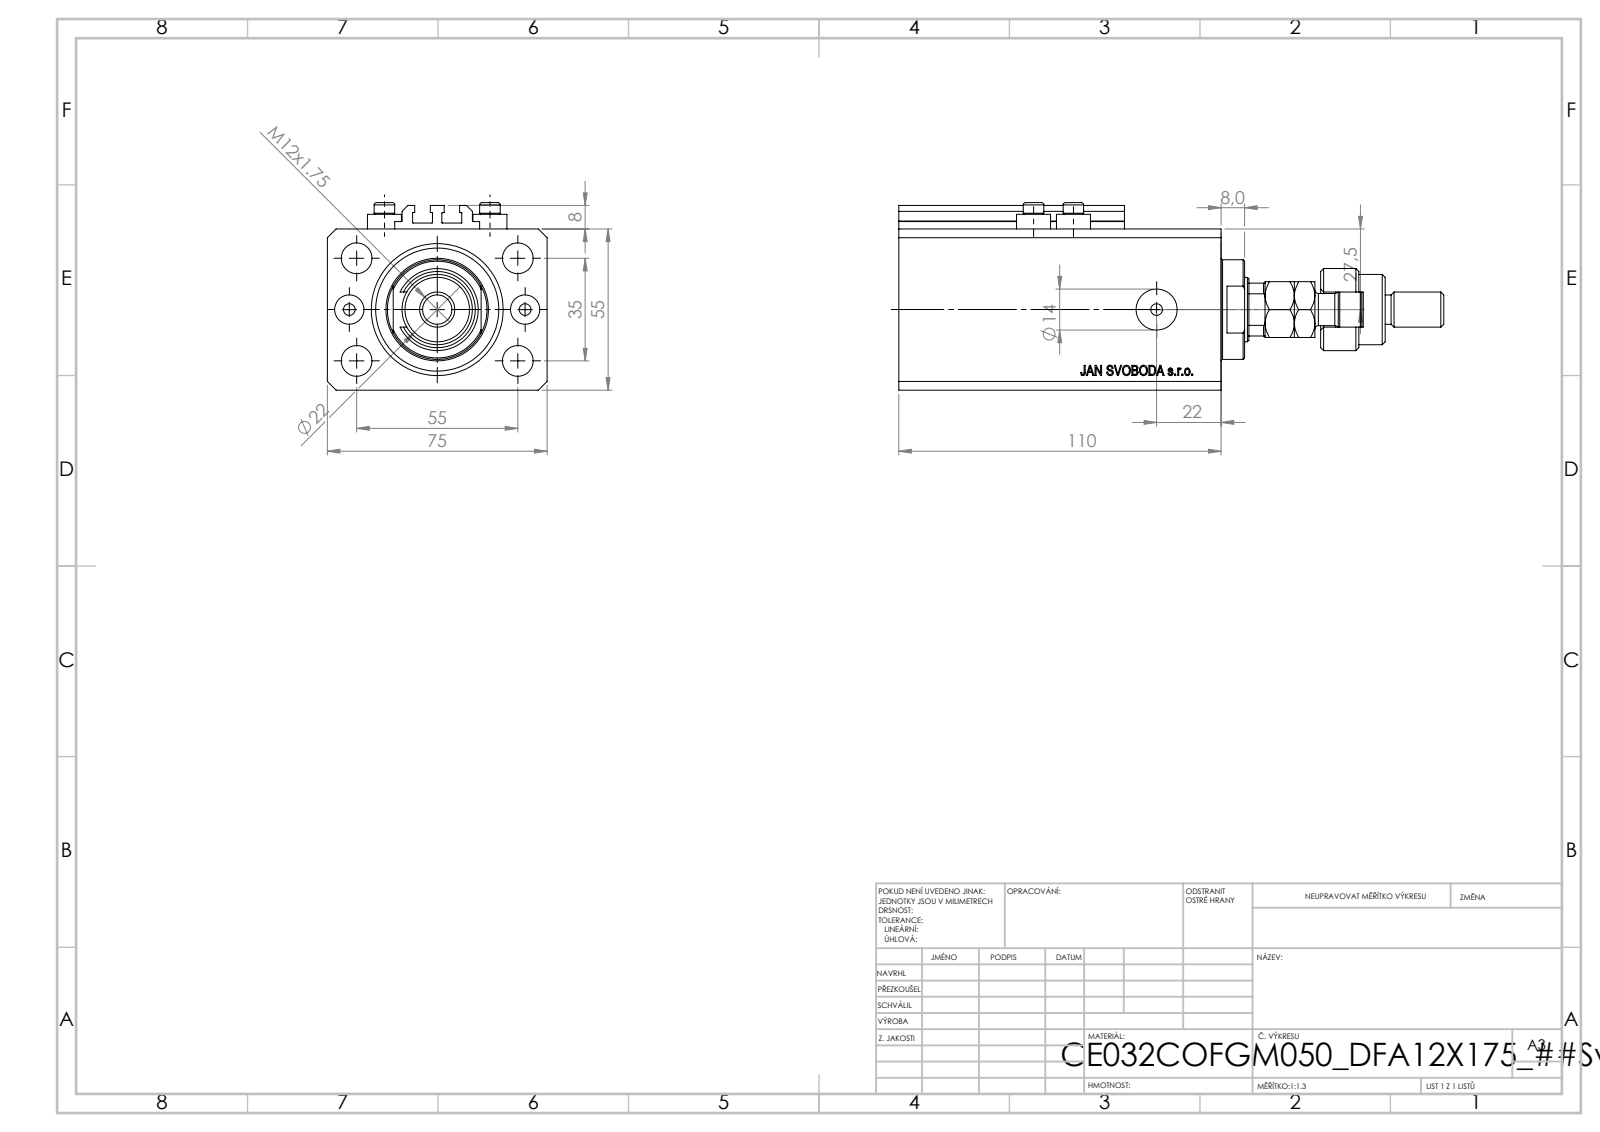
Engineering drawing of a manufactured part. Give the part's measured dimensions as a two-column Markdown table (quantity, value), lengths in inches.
| quantity | value |
| --- | --- |
| part name | V250CE_C_Body; V250CE_VC_C; ALLEN BOLT V250CE; V250CE_C_VCP (+2 more) |
| STEP written by | SolidWorks 2019 (CONFIG_CONTROL_DESIGN) |
| units | inches |
| bodies | 10 solids, 1119 faces (532 planar, 99 cylindrical, 488 other) |
| overall size | 7.323 × 2.953 × 2.52 |
| volume | 26.05 in³ |
| surface area | 152.3 in² |
| round holes (diameter × count) | 0.157 × 8, 0.413 × 5, 0.394 × 2, 0.551 × 2, 0.866 × 1, 1.26 × 1, 1.772 × 1 |
| round bosses / shafts (diameter × count) | 0.457 × 4, 0.276 × 4, 1.339 × 1, 1.102 × 1, 0.945 × 1, 0.709 × 1, 0.472 × 1, 0.433 × 1 |
| partial cylindrical surfaces (radius × count) | 0.008 × 10, 0.384 × 1, 0.413 × 1 |
| main face-to-face distances | 2.165, 2.953, 0.591, 4.331, 3.74, 0.39, 0.315, 3.35, 3.941, 0.118 |
| hole center spacings | 0.696, 1.283, 2.366, 0.535, 1.181, 1.378, 1.417, 1.515 |
